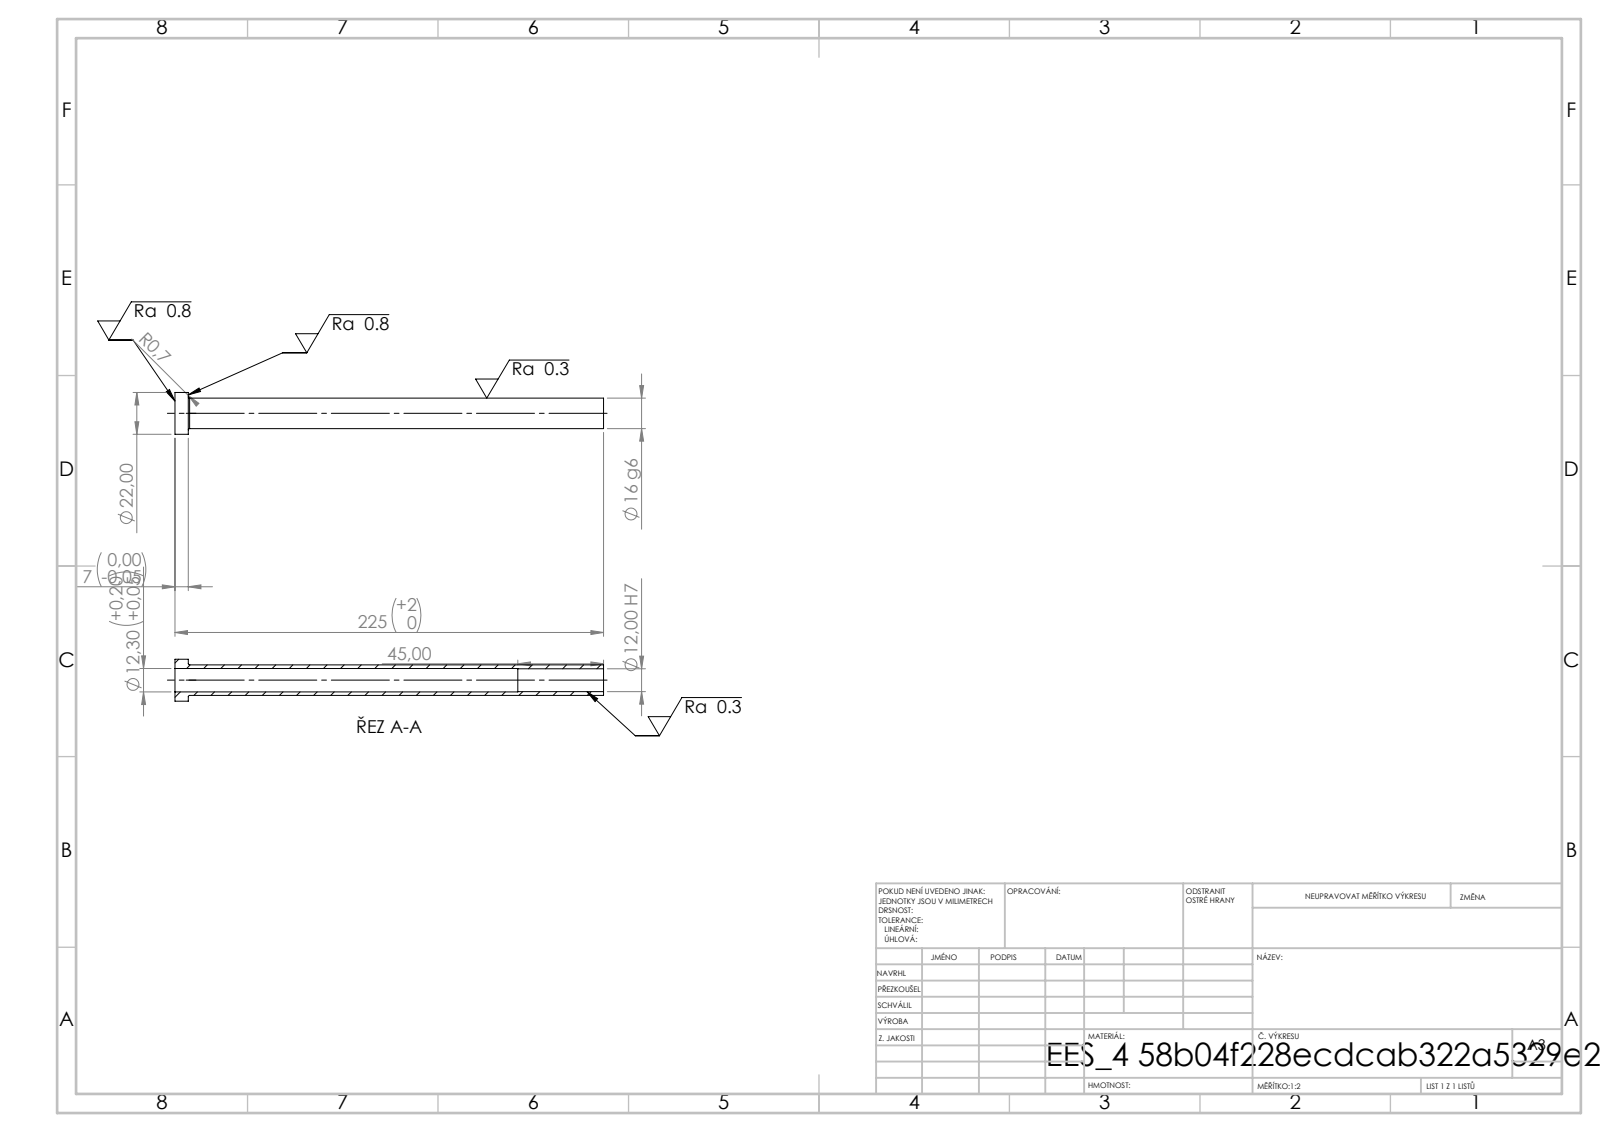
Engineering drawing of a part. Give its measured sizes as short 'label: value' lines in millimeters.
written by: SolidWorks 2019 (CONFIG_CONTROL_DESIGN)
unit: mm
bodies: 1 solid, 14 faces (4 planar, 8 cylindrical, 2 other)
size: 225 × 22 × 22
volume: 20 020 mm³; area: 20 613 mm²
holes: 1× ⌀12, 1× ⌀12.3
bosses: 1× ⌀22, 1× ⌀16
face distances: 7, 225, 218, 180, 173, 45
